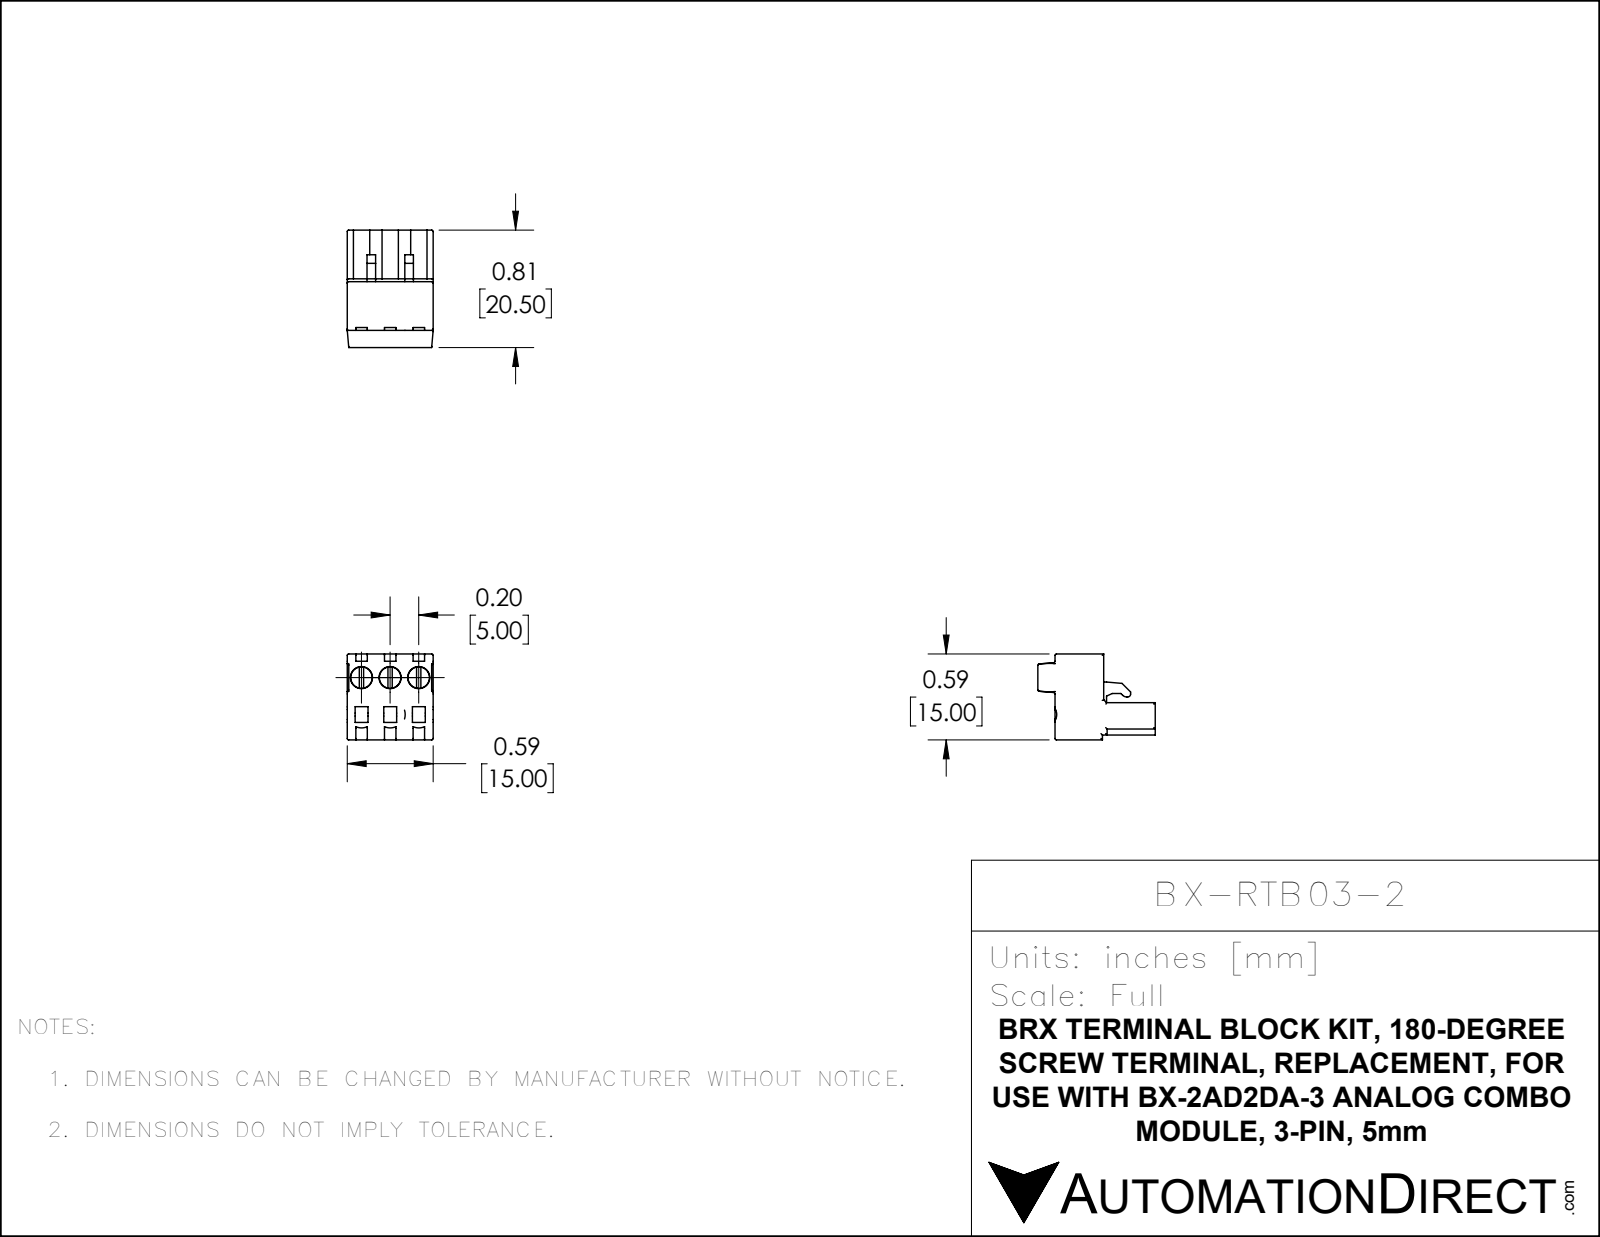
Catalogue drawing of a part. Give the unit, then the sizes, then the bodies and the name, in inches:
Units: inches
Overall size (bounding box): 0.807 × 0.591 × 0.591
Round holes (diameter × count): ⌀0.063 ×3, ⌀0.124 ×3, ⌀0.152 ×3
Round bosses / shafts (diameter × count): ⌀0.148 ×3
Partial cylindrical surfaces — rounded edges, fillets, slot ends (radius × count): R0.01 ×34, R0.092 ×3, R0.099 ×3, R0.02 ×1, R0.039 ×1
Main face-to-face distances: 0.591, 0.335, 0.224, 0.366, 0.354, 0.256, 0.031, 0.689, 0.059, 0.108
Hole centre spacings: 0.197, 0.295, 0.354, 0.355, 0.394, 0.491, 0.493
Volume: 0.154 in³ · Surface area: 3.149 in²
Bodies: 1 solid, 264 faces (143 planar, 78 cylindrical, 43 other)
Part name (STEP PRODUCT): BX-RTB03-2
STEP written by: SolidWorks 2021 (AUTOMOTIVE_DESIGN)
